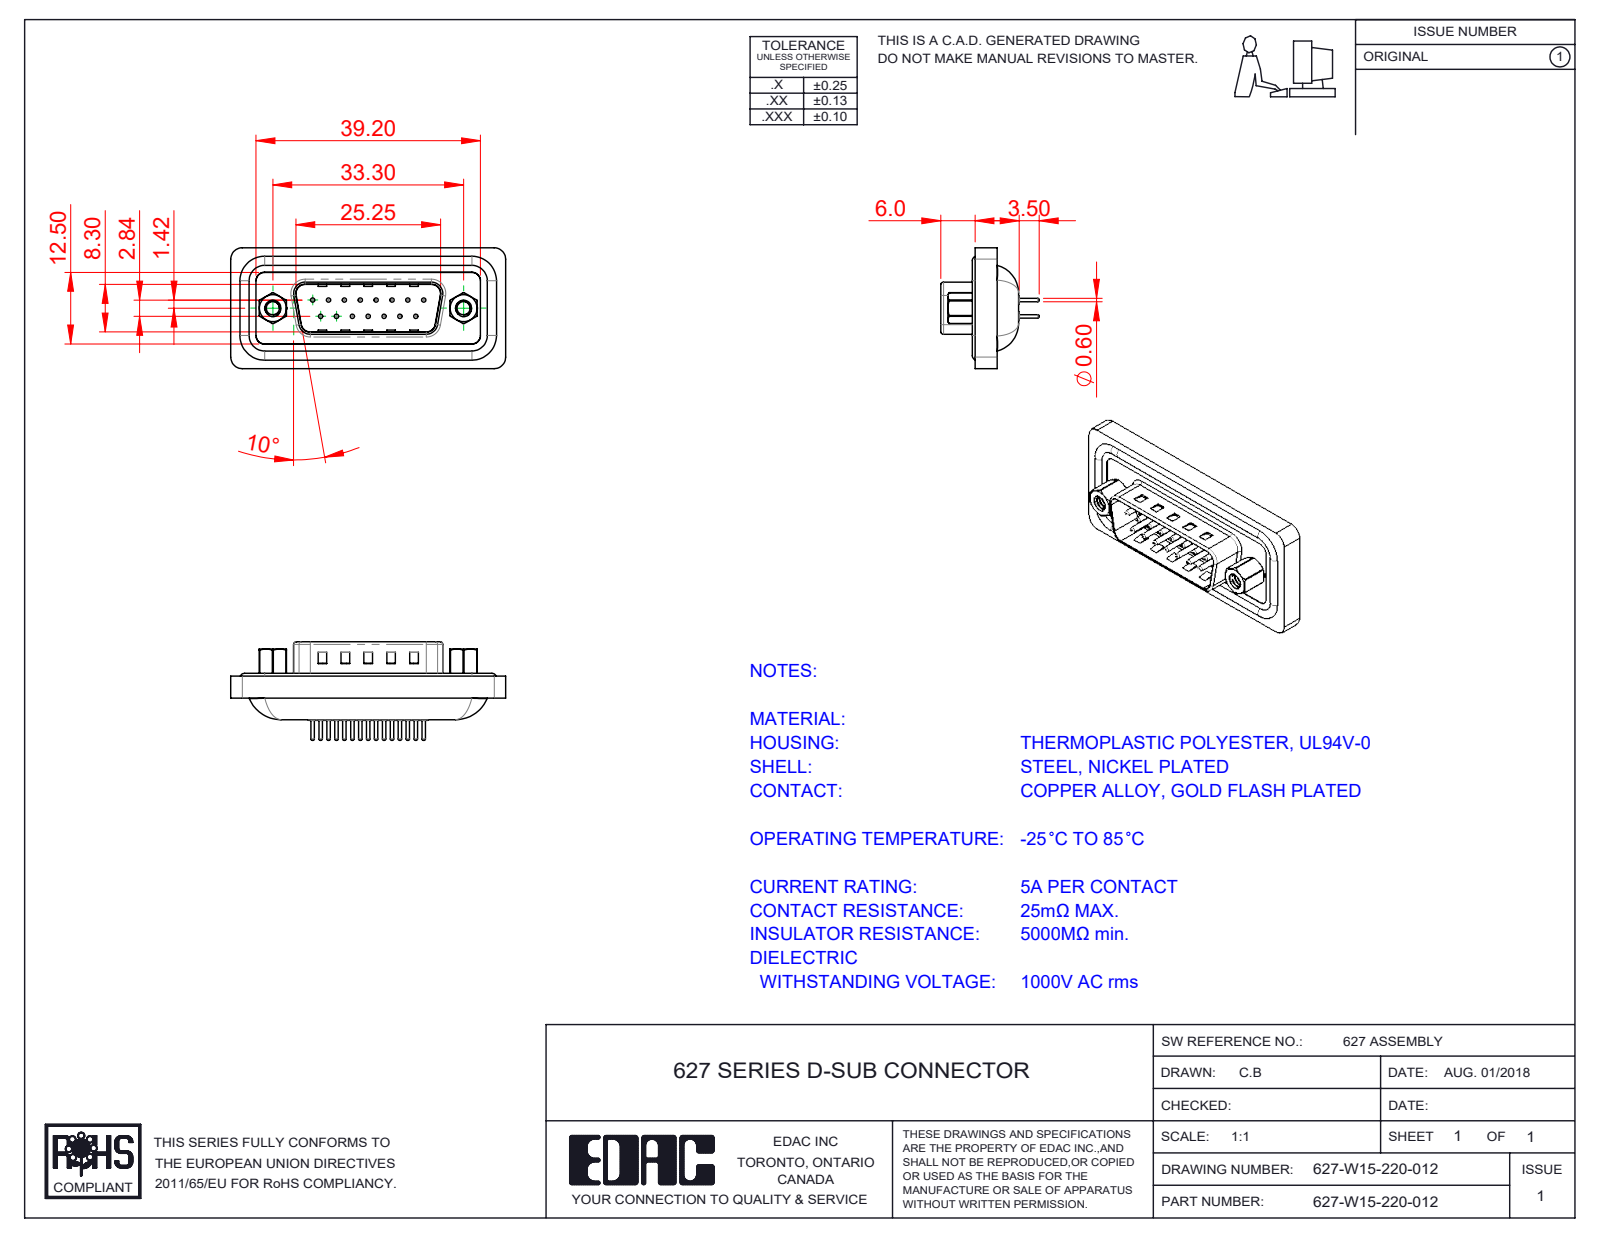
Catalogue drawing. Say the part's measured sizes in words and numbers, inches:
The part is named "627W Contact Row 1_20; 627-W15-220-012; 627W 4-40 Threaded Rivet; 627W Waterproof Housing_15 Contacts (+4 more)". Its 3-D file was written by "SolidWorks 2020 (CONFIG_CONTROL_DESIGN)". It is 23 solids with 1069 faces: 278 planar, 456 cylindrical and 335 other. Overall it measures 1.89 by 0.831 by 0.677 inches. Its volume is 0.351 cubic inches and its surface area 12.83 square inches. Round holes: 15 of diameter 0.03, 15 of diameter 0.059, 15 of diameter 0.063, 15 of diameter 0.079, 2 of diameter 0.089, 2 of diameter 0.09, 2 of diameter 0.157, 2 of diameter 0.189, 2 of diameter 0.197. Round bosses or shafts: 15 of diameter 0.024, 7 of diameter 0.059, 4 of diameter 0.063, 2 of diameter 0.193, 2 of diameter 0.11. Partial cylindrical surfaces (rounded edges, fillets, slot ends): 16 of radius 0.079, 14 of radius 0.059, 8 of radius 0.02, 6 of radius 0.106, 4 of radius 0.035, 4 of radius 0.063, 4 of radius 0.169, 2 of radius 0.016. The main face-to-face distances are 0.03, 0.016, 0.043, 0.108, 0.148, 0.02, 0.073, 0.181, 0.063, 0.039. The hole center spacings are 0.124, 0.109, 0.218, 0.327, 0.198, 0.198, 0.294, 0.295.
